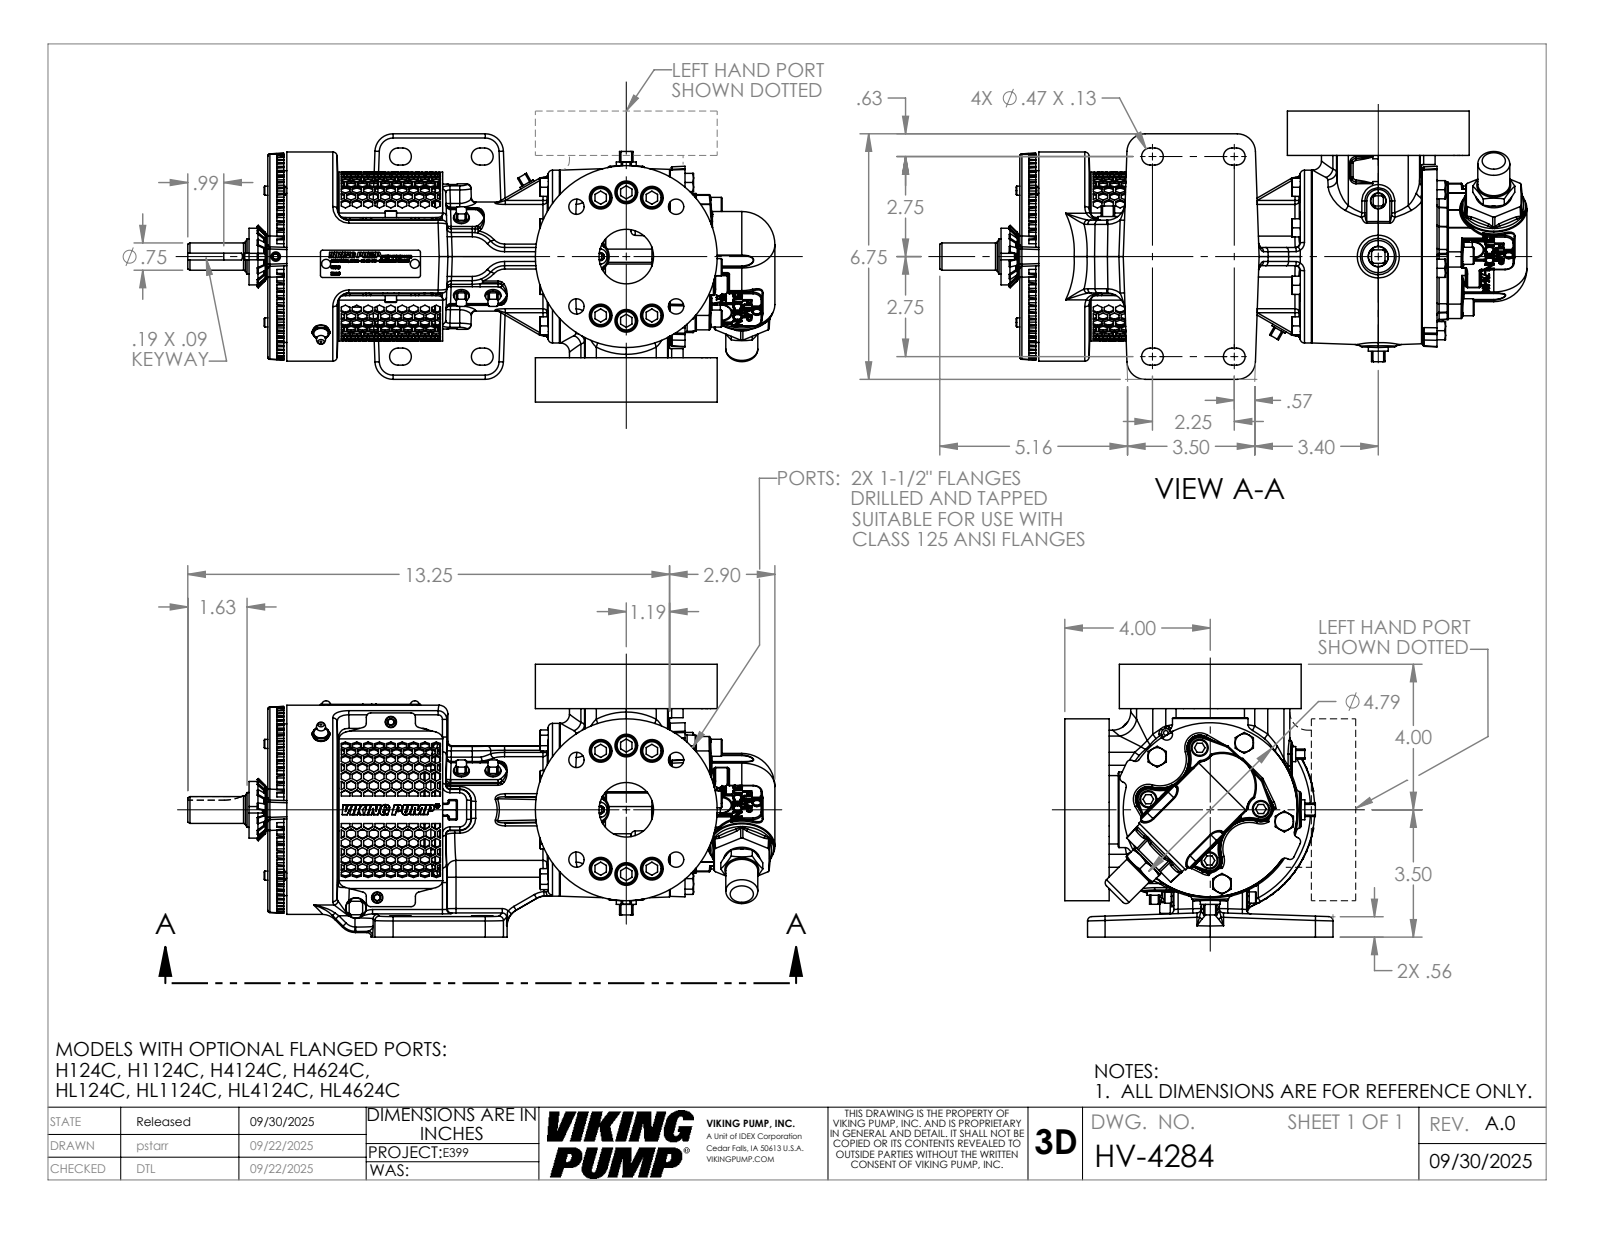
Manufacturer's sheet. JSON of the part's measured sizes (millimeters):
{"part_name": "HV-4284", "step_written_by": "SolidWorks 2024 (AUTOMOTIVE_DESIGN)", "units": "millimeters", "bodies": {"solids": 1, "faces": 5129, "planar": 1883, "cylindrical": 1020, "other": 2226}, "overall_size": [410.08, 190.5, 187.32], "volume_mm3": 3940000, "surface_area_mm2": 412364, "round_holes": [[6.35, 9], [15.88, 9], [10.72, 8], [8.64, 4], [8.74, 4], [4.04, 3], [5.02, 3], [15.87, 3], [6.53, 2], [38.1, 2], [25.03, 1], [25.12, 1]], "round_bosses_or_shafts": [[14.29, 12], [11.91, 4], [7.95, 4], [7.92, 3], [4.83, 3], [127, 2], [6.35, 2], [146.05, 1]], "partial_cylinders_radius": [[1.37, 140], [3.05, 104], [0.76, 94], [1.52, 54], [12.7, 34], [6.1, 11], [5.95, 8], [6.35, 8]], "face_to_face_distances": [30.99, 190.5, 49.28, 291.43, 242.15, 159.51, 13.3, 35.98, 278.13, 38.1], "hole_center_spacings": [44.85, 65.03, 18.07, 18.26, 36.22, 49.21, 53.06, 69.6]}
